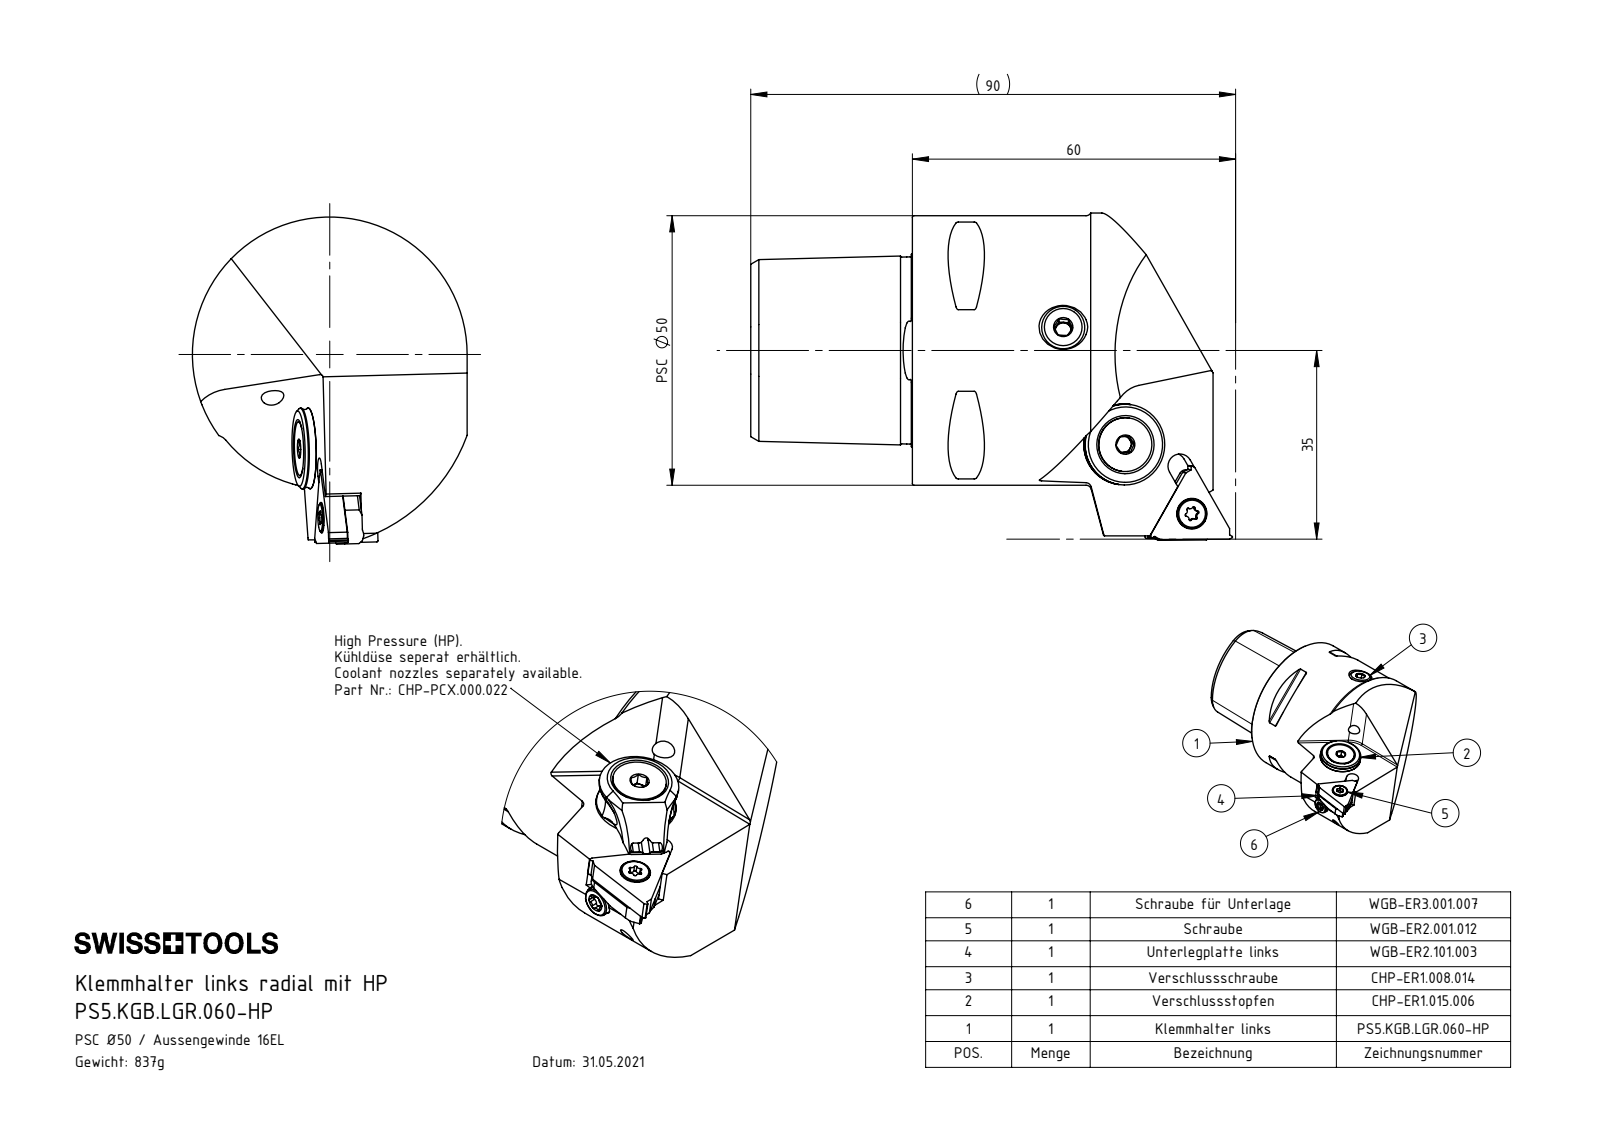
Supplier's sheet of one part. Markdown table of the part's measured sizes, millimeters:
| quantity | value |
| --- | --- |
| part name | LT16EL; DIN 7991 - M5x15; CHP-ER1.015.006_A; DIN 3771 - 13x1 (+8 more) |
| STEP written by | SolidWorks 2017 (AUTOMOTIVE_DESIGN) |
| units | millimeters |
| bodies | 10 solids, 312 faces (127 planar, 86 cylindrical, 99 other) |
| overall size | 89.41 × 60.5 × 51 |
| volume | 107 558 mm³ |
| surface area | 23 314 mm² |
| round holes (diameter × count) | 4.2 × 3, 2.58 × 2, 4 × 2, 1.2 × 1, 2 × 1, 2.5 × 1, 3 × 1, 4.02 × 1, 5 × 1, 5.2 × 1, 6.1 × 1, 7 × 1 |
| round bosses / shafts (diameter × count) | 5.5 × 3, 50 × 1, 15 × 1, 13.4 × 1, 10 × 1, 8 × 1, 5 × 1, 3.18 × 1 |
| partial cylindrical surfaces (radius × count) | 0.5 × 10, 0.23 × 6, 0.34 × 6, 0.57 × 6, 0.57 × 6, 0.1 × 2, 0.25 × 2, 1.3 × 1 |
| main face-to-face distances | 30, 4.79, 19.18, 1.45, 3.34, 1.74, 3.19, 6.53, 44.4, 6.84 |
| hole center spacings | 4.53, 19.83, 4.5, 4.56, 17.02, 17.04, 17.05, 17.07 |
